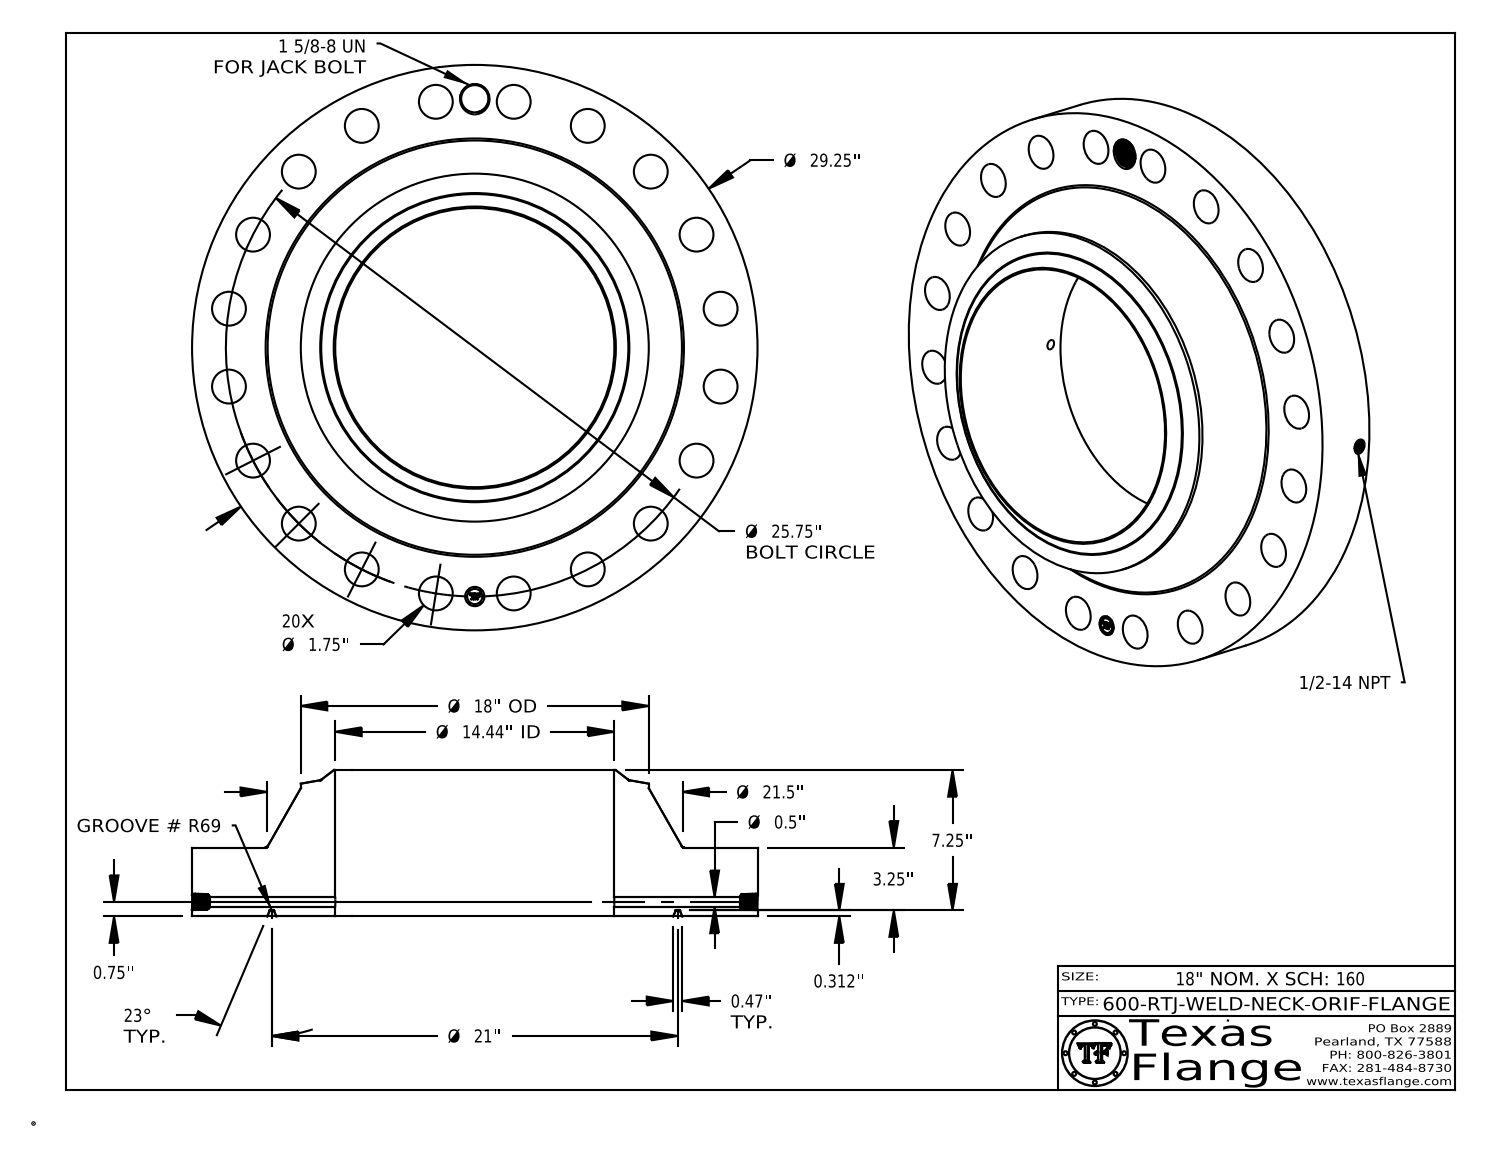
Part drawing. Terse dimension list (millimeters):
name: 600-RTJ-WELD-NECK
written by: CATIA V5 STEP AP214 (AUTOMOTIVE_DESIGN)
unit: mm
bodies: 1 solid, 885 faces (370 planar, 142 cylindrical, 373 other)
size: 743 × 743 × 192.1
volume: 34 490 000 mm³; area: 1 418 000 mm²
holes: 20× ⌀44.5, 1× ⌀12.7, 1× ⌀17.1, 1× ⌀25.4, 1× ⌀35.8, 1× ⌀366.7
bosses: 8× ⌀1.5, 1× ⌀743, 1× ⌀457.2, 1× ⌀20
face distances: 90.5, 7.9, 82.6, 192.1, 184.2, 101.6, 0.4, 90.1, 82.2, 102
hole spacings: 384.4, 622, 646, 327, 296.9, 102.3, 202.1, 462.5
